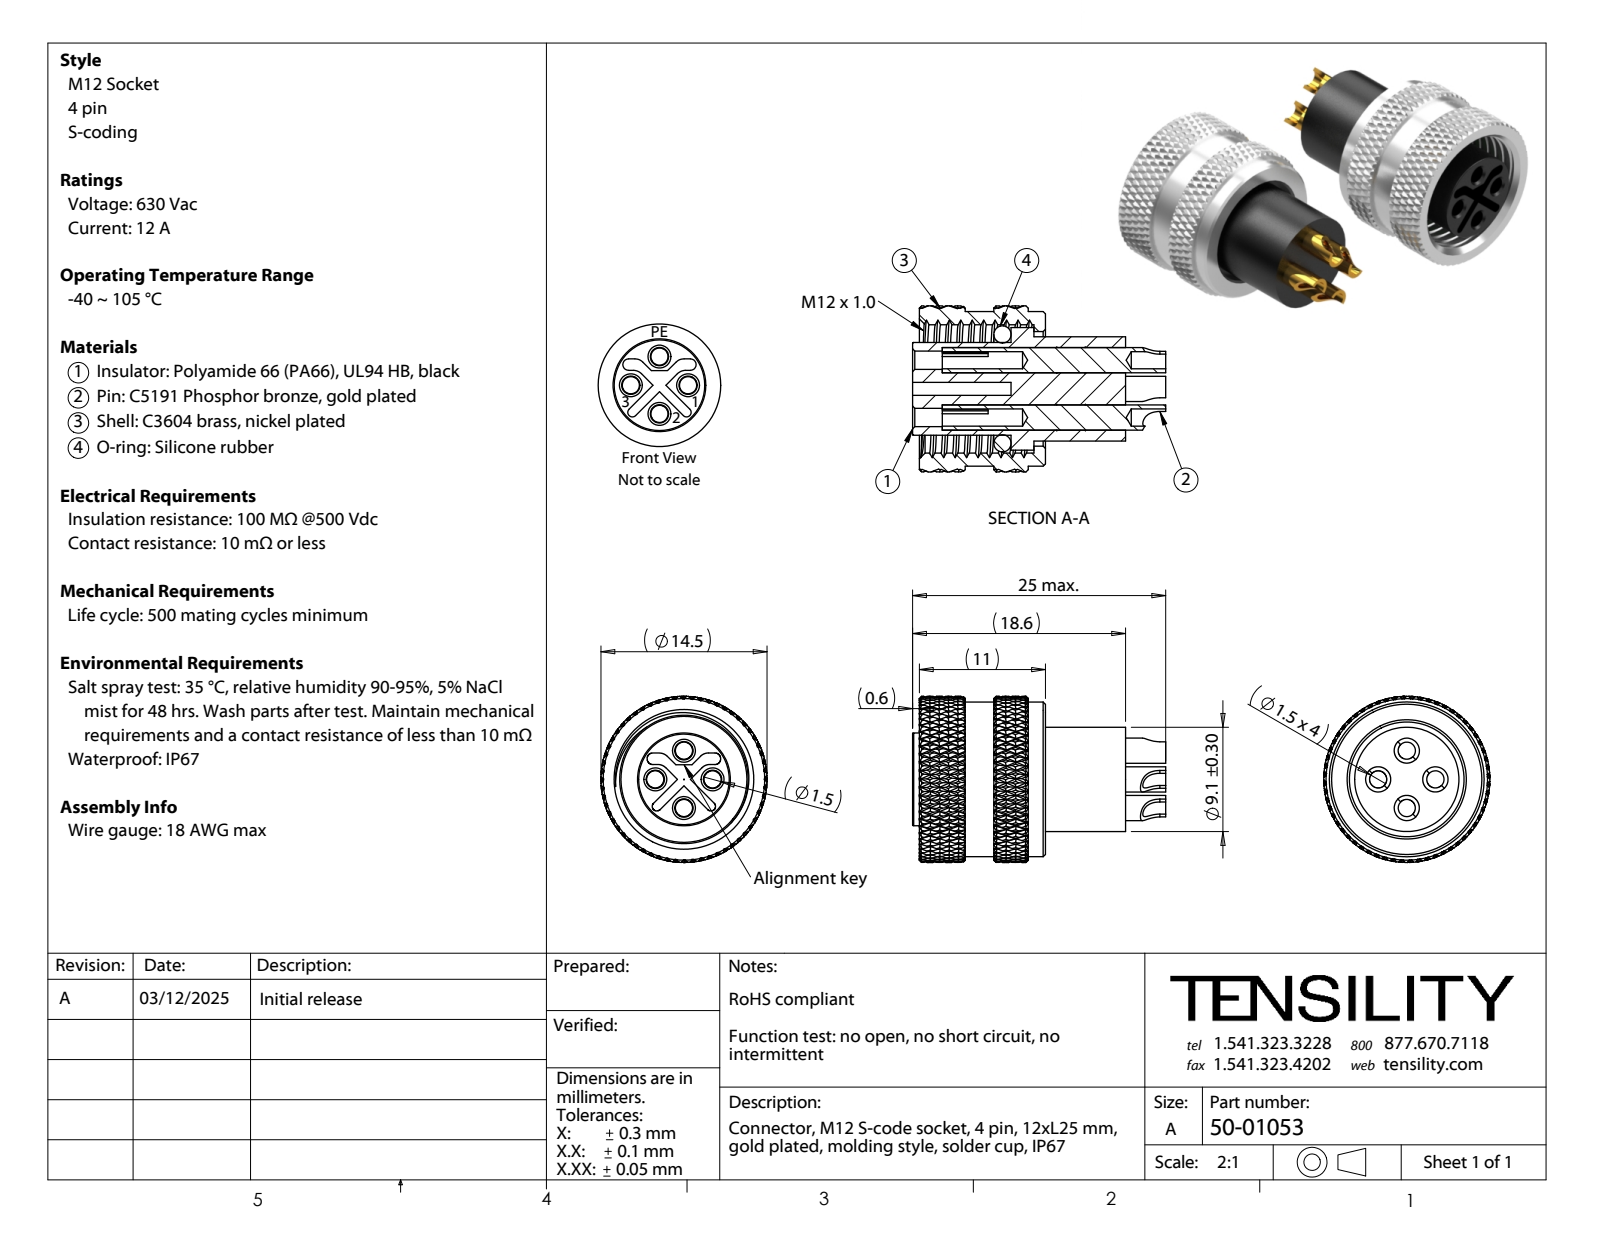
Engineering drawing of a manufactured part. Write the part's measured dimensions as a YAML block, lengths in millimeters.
part_name: "50-01053-02_step; 50-01053-04; 50-01053-03; 50-01053-01 (+1 more)"
step_written_by: "SolidWorks 2021 (CONFIG_CONTROL_DESIGN)"
units: millimeters
bodies: {solids: 7, faces: 249, planar: 81, cylindrical: 106, other: 62}
overall_size: [22.1, 14.5, 14.5]
volume: 1660
surface_area: 3489
round_holes:
  - {diameter: 1.5, count: 4}
  - {diameter: 1.6, count: 4}
  - {diameter: 10, count: 1}
  - {diameter: 11.2, count: 1}
round_bosses_or_shafts:
  - {diameter: 2.2, count: 4}
  - {diameter: 14.5, count: 1}
  - {diameter: 13.5, count: 1}
  - {diameter: 10.7, count: 1}
  - {diameter: 9.1, count: 1}
  - {diameter: 8.1, count: 1}
partial_cylinders:
  - {radius: 1, count: 4}
  - {radius: 0.4, count: 2}
  - {radius: 0.5, count: 2}
  - {radius: 1.86, count: 2}
face_to_face_distances: [8, 10, 2, 0.8, 7, 3, 1, 11, 18, 1.5]
hole_center_spacings: [2.5, 3.54, 5]
